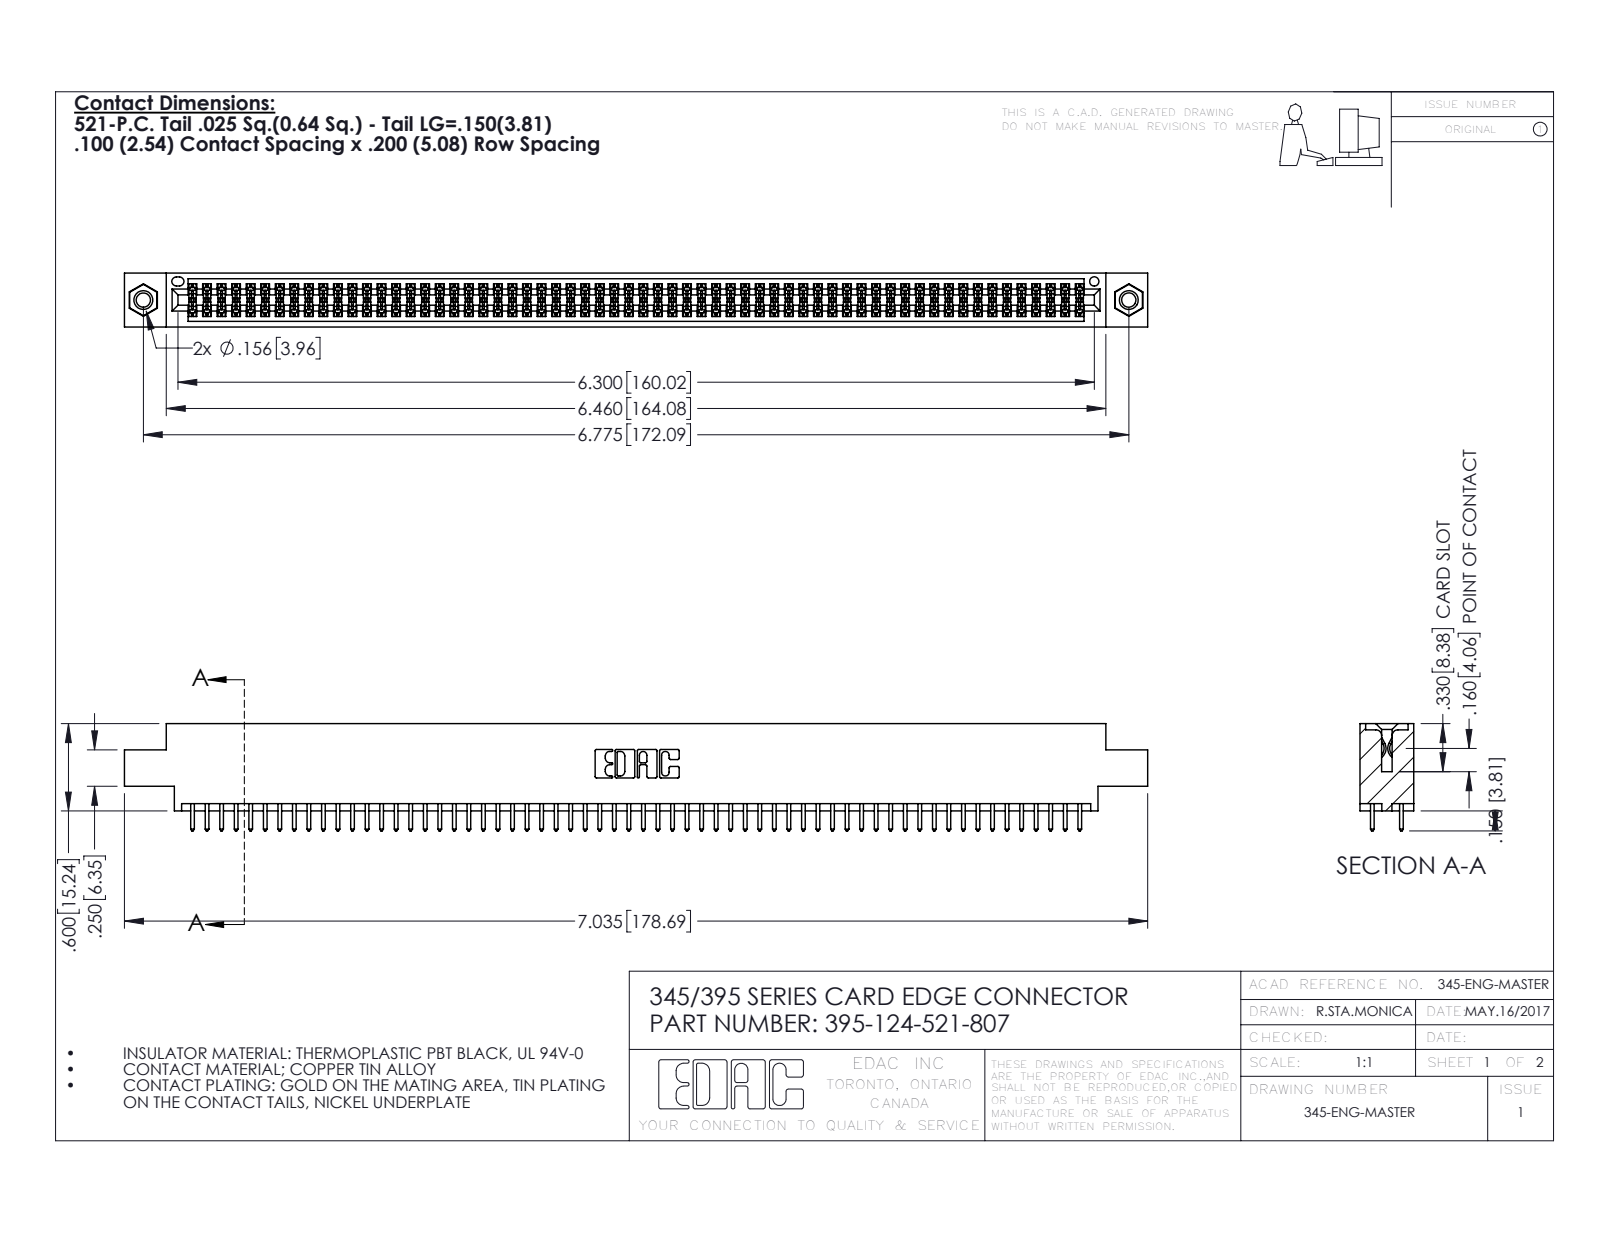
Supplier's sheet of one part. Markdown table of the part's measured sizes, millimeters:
| quantity | value |
| --- | --- |
| part name | 345-292-001_345-293-121; 345-250-001_345-250-005-103; 345 Part_0.170 Offset - 0.156 Dia-TI; 395-124-521-807 |
| STEP written by | SolidWorks 2016 (CONFIG_CONTROL_DESIGN) |
| units | millimeters |
| bodies | 127 solids, 6390 faces (4208 planar, 2166 cylindrical, 16 other) |
| overall size | 178.7 × 18.7 × 9.4 |
| volume | 17 370 mm³ |
| surface area | 25 900 mm² |
| round holes (diameter × count) | 2.5 × 2, 3.2 × 2, 4 × 2, 1.6 × 1 |
| round bosses / shafts (diameter × count) | 3.9 × 2 |
| partial cylindrical surfaces (radius × count) | 0.2 × 186, 0.3 × 124, 0.3 × 22, 0.2 × 6, 0.8 × 6, 0.7 × 3, 0.4 × 2, 0.5 × 2 |
| main face-to-face distances | 1.8, 7.6, 5.1, 9.4, 2.5, 6.9, 0.6, 5.7, 4.4, 3.8 |
| hole center spacings | 6.9, 166.1, 172.1 |
